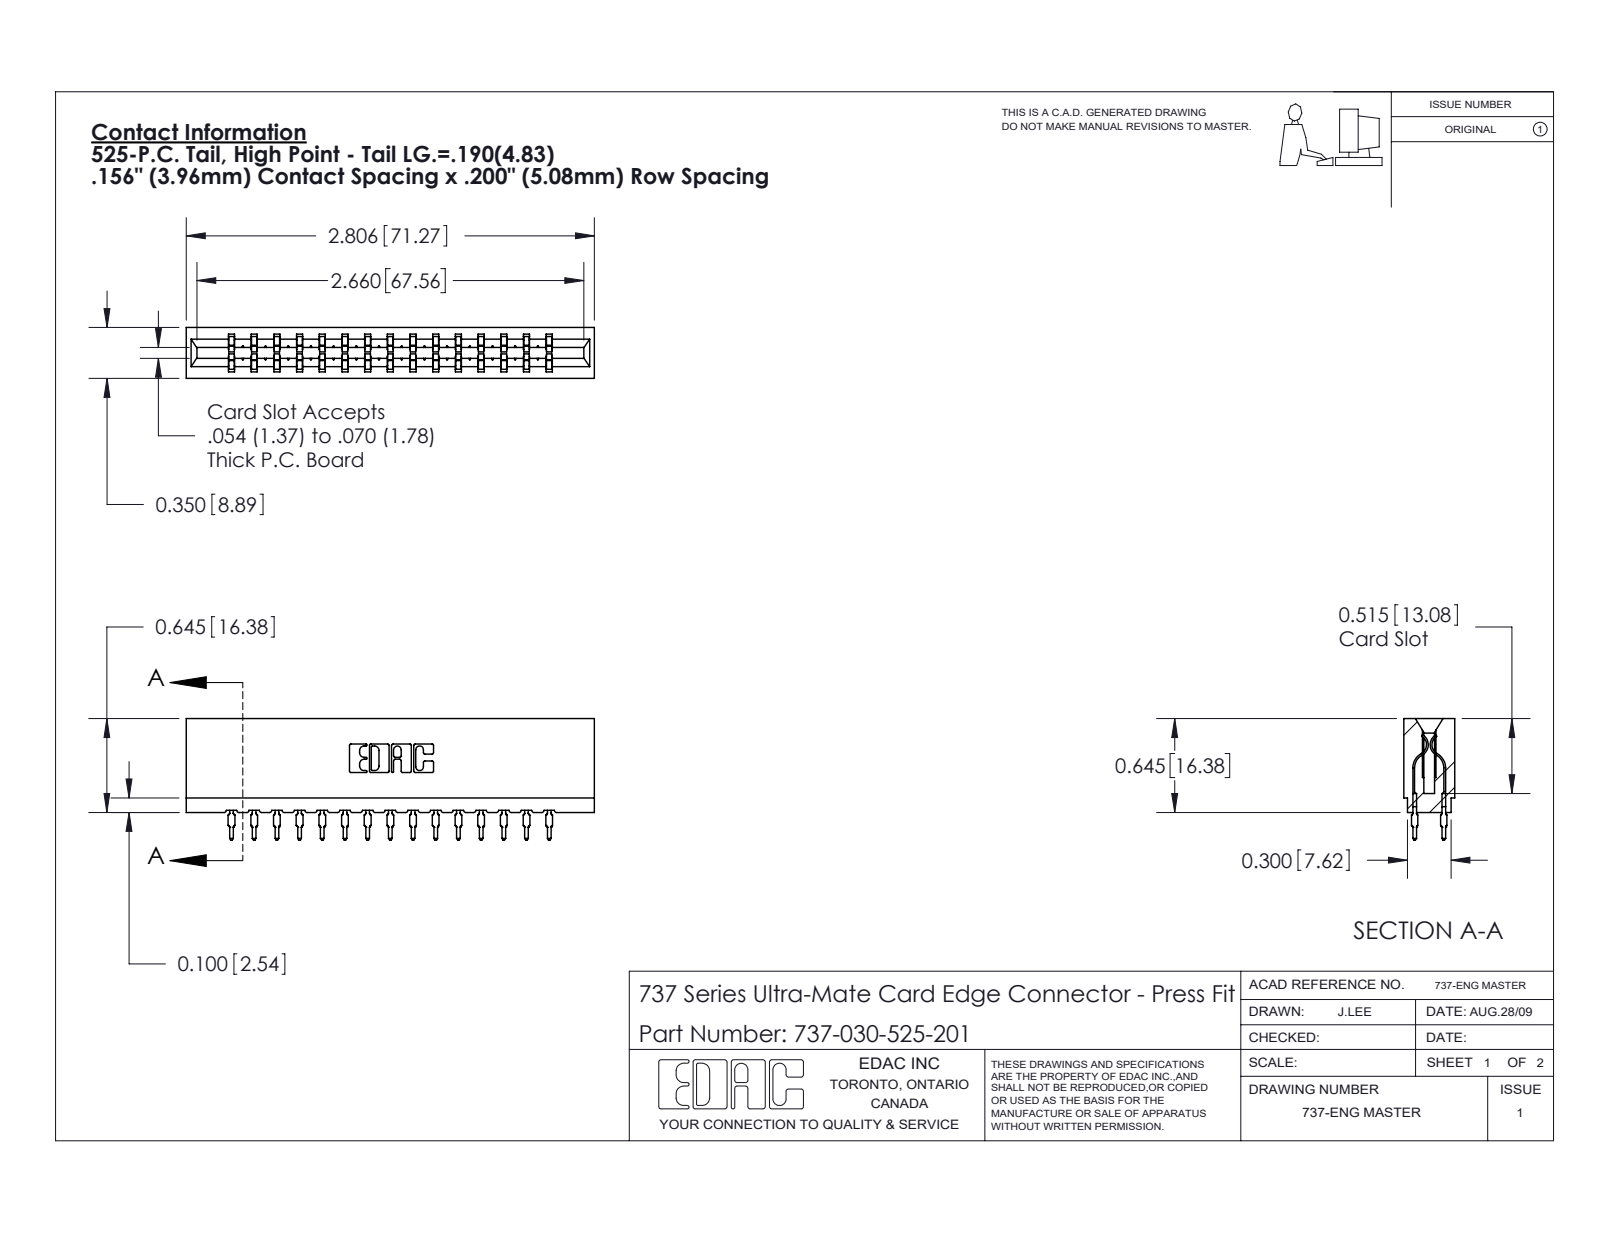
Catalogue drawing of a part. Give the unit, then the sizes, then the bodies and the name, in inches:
Units: inches
Overall size (bounding box): 2.806 × 0.836 × 0.35
Partial cylindrical surfaces — rounded edges, fillets, slot ends (radius × count): R0.021 ×60, R0.015 ×30, R0.01 ×22, R0.005 ×8, R0.011 ×8, R0.007 ×6, R0.031 ×6, R0.026 ×3
Main face-to-face distances: 0.138, 0.212, 0.35, 0.156, 0.624, 0.312, 0.468, 0.074, 0.78, 0.063
Volume: 0.44 in³ · Surface area: 15.25 in²
Bodies: 31 solids, 2794 faces (1449 planar, 565 cylindrical, 780 other)
Part name (STEP PRODUCT): 737-030-525-201; 745-292-001_525; 737 Part_Insulator Option - 01
STEP written by: SolidWorks 2020 (CONFIG_CONTROL_DESIGN)
